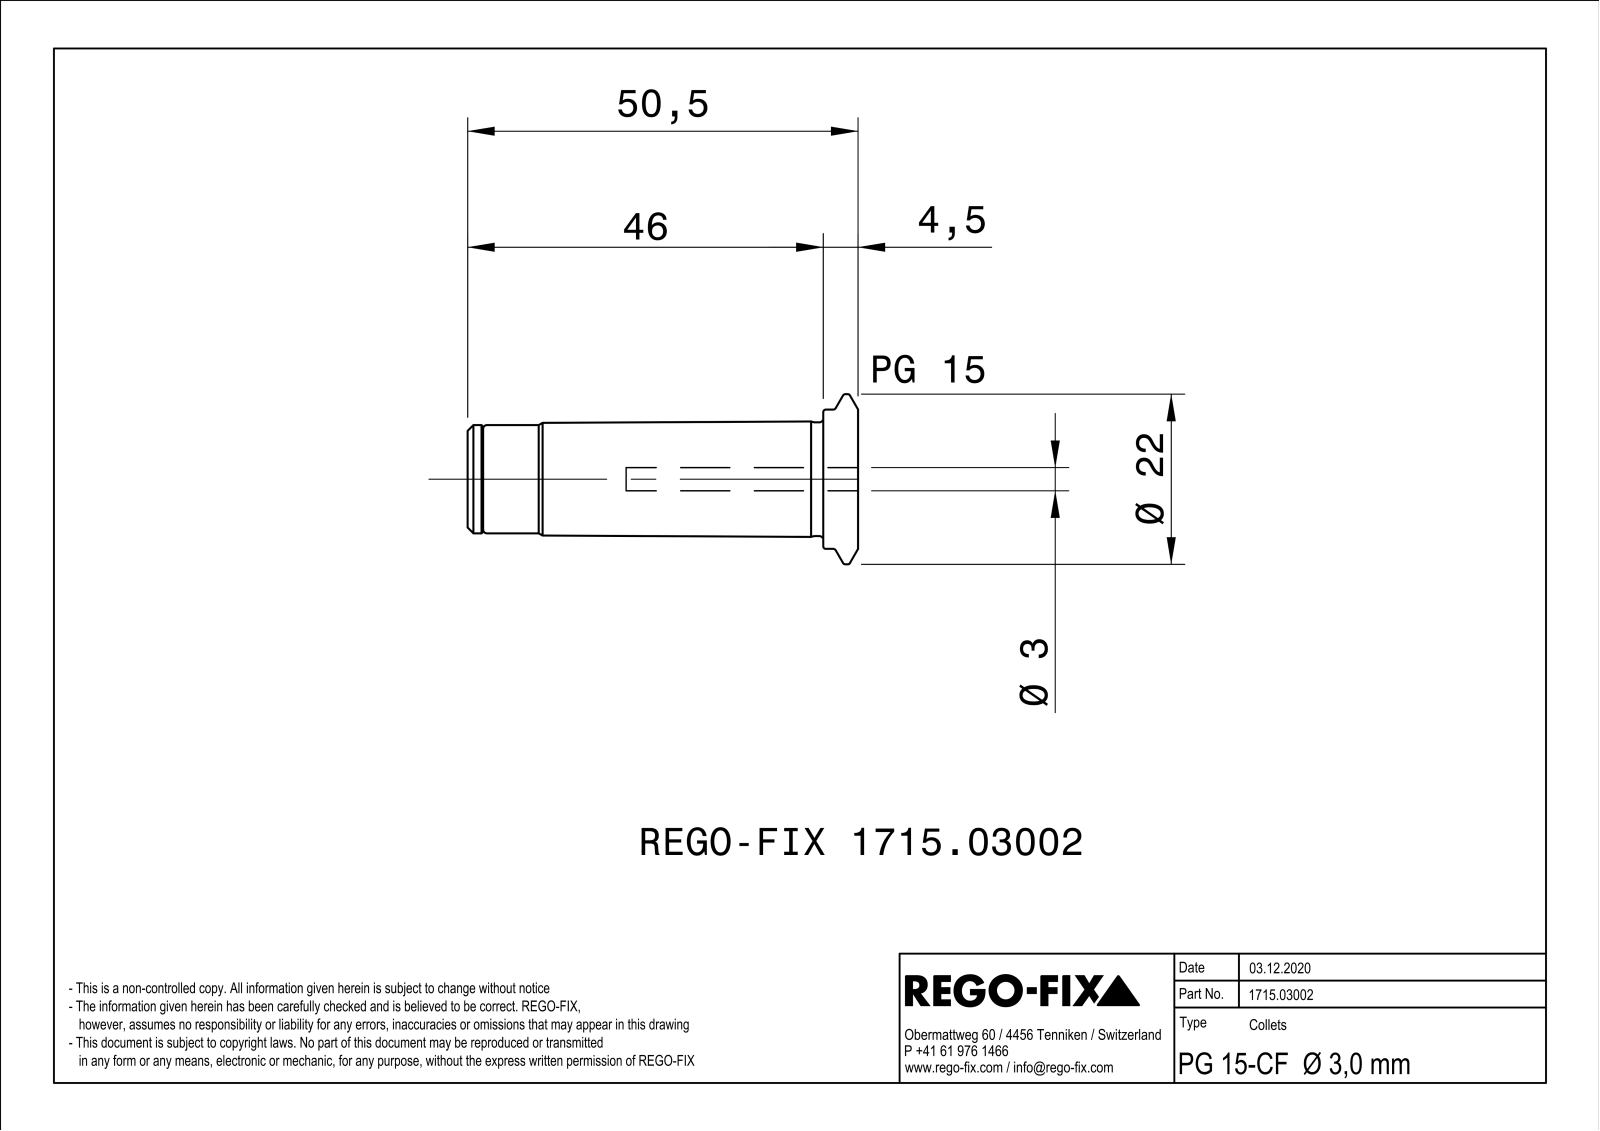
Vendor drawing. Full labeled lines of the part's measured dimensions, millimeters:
Part name (STEP PRODUCT): NOCUT
STEP written by: SIEMENS PLM Software Solid Edge ST10 (AUTOMOTIVE_DESIGN)
Units: millimetres
Bodies: 1 solid, 124 faces (41 planar, 31 cylindrical, 52 other)
Overall size (bounding box): 50.5 × 22 × 21.99
Volume: 7 136 mm³ · Surface area: 5 354 mm²
Round holes (diameter × count): ⌀5.2 ×1, ⌀6.92 ×1, ⌀8.2 ×1, ⌀8.5 ×1, ⌀10.92 ×1, ⌀12.2 ×1
Round bosses / shafts (diameter × count): ⌀22 ×1, ⌀18 ×1, ⌀14.7 ×1, ⌀14 ×1
Partial cylindrical surfaces — rounded edges, fillets, slot ends (radius × count): R0.5 ×3, R1.5 ×1, R5.2 ×1, R6 ×1
Main face-to-face distances: 1, 2, 50.5, 40.5, 10, 41.5, 9, 3, 4.5, 36
